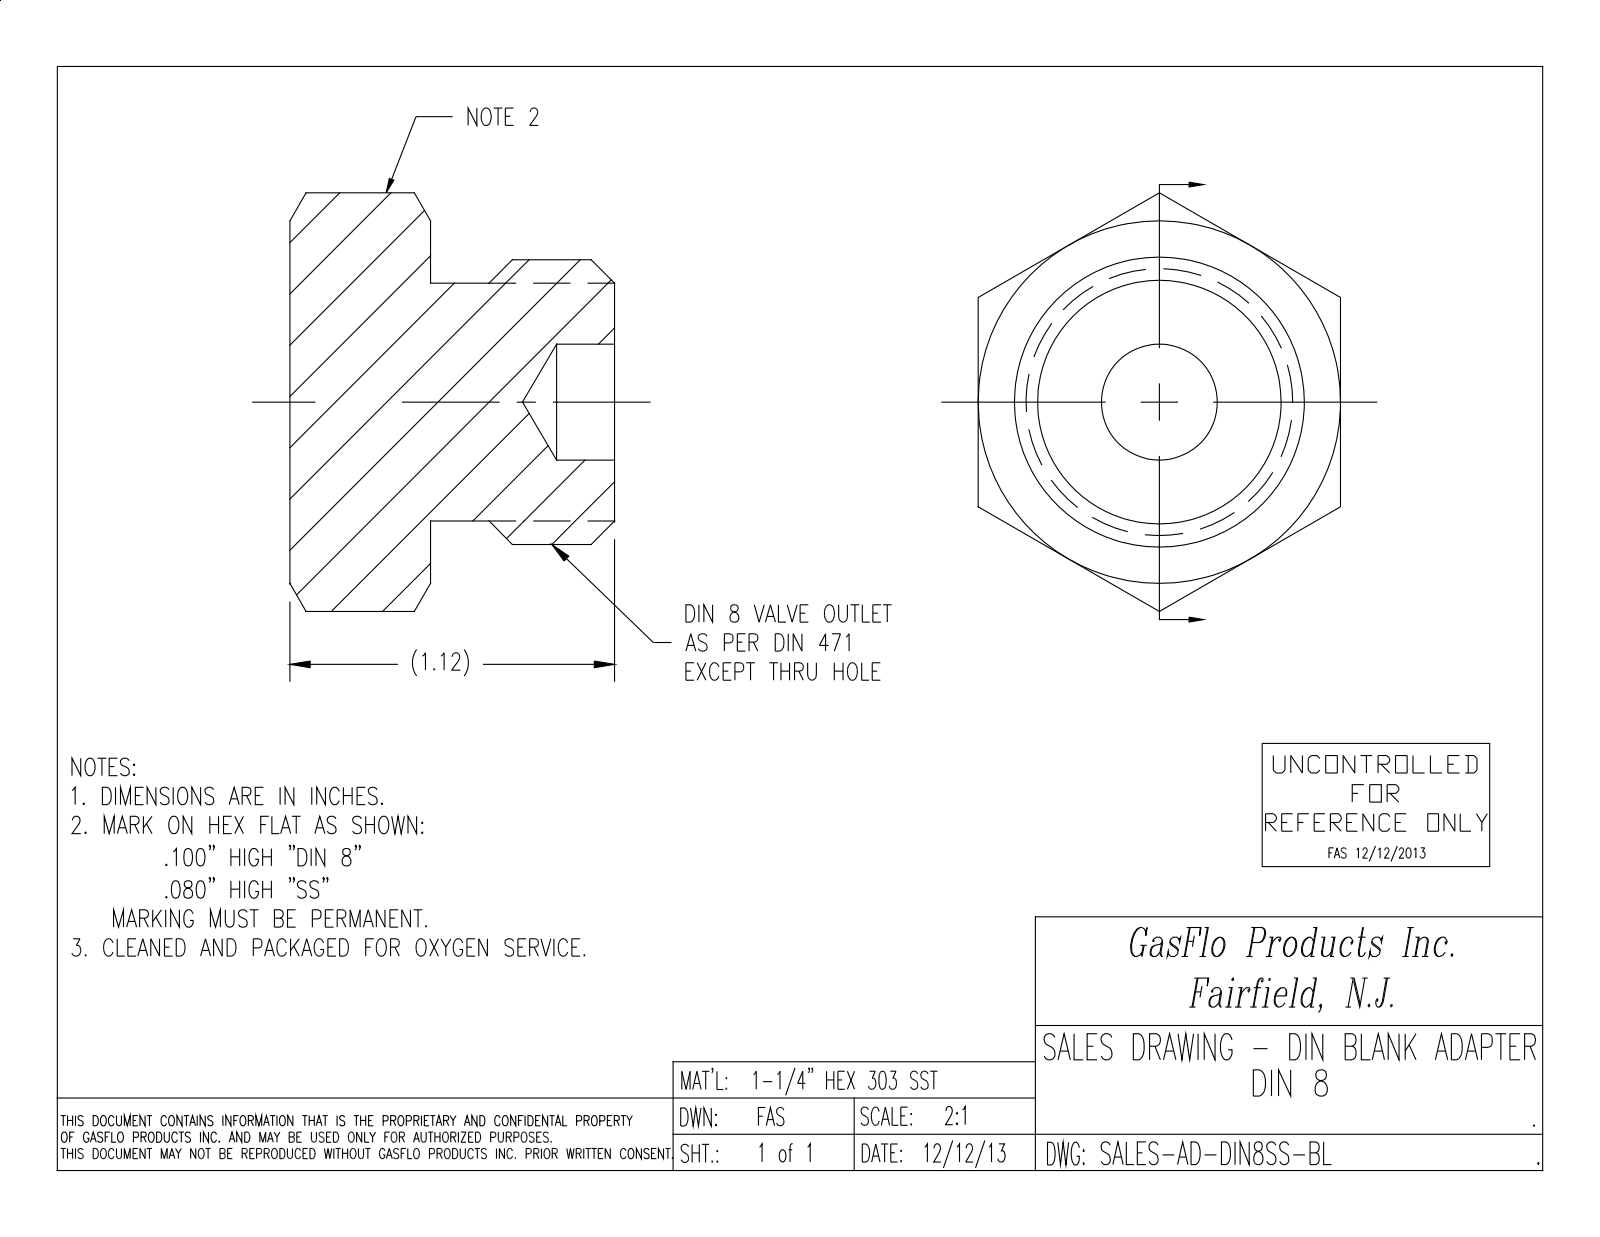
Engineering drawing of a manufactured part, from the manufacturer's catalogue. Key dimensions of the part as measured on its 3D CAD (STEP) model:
Part name (STEP PRODUCT): AD-DIN8SS-BL
STEP written by: SolidWorks 2018 (CONFIG_CONTROL_DESIGN)
Units: inches
Bodies: 1 solid, 125 faces (43 planar, 10 cylindrical, 72 other)
Overall size (bounding box): 1.443 × 1.25 × 1.12
Volume: 0.994 in³ · Surface area: 7.686 in²
Round holes (diameter × count): ⌀0.4 ×1
Round bosses / shafts (diameter × count): ⌀0.994 ×1, ⌀0.82 ×1
Main face-to-face distances: 0.485, 1.25, 1.12, 0.635, 1.25, 1.245, 0.024, 0.081, 0.078, 0.105
